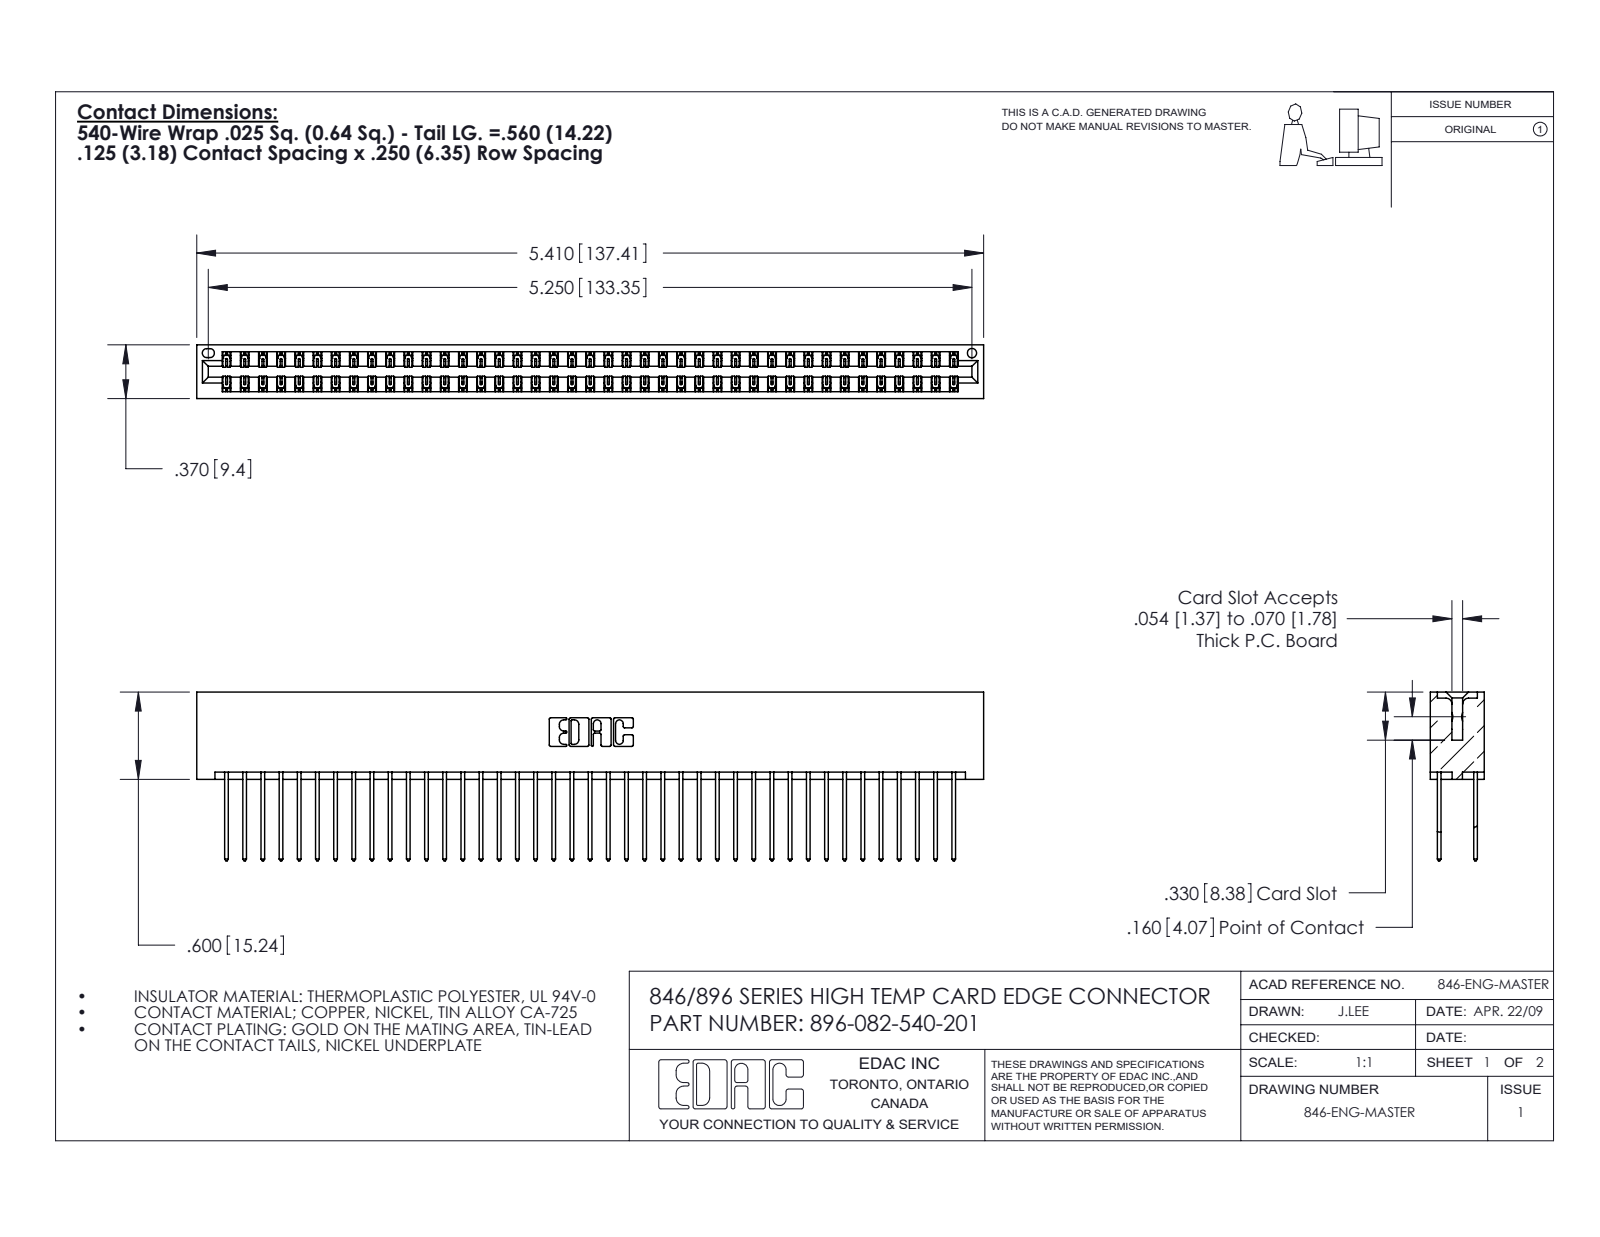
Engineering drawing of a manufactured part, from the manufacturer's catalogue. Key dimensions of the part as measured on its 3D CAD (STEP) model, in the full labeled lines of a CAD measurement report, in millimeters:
Part name (STEP PRODUCT): 396-082-540-201; 346 Part_No Mounting Lugs; 345-292-001_345-293-140
STEP written by: SolidWorks 2016 (CONFIG_CONTROL_DESIGN)
Units: millimetres
Bodies: 83 solids, 4378 faces (2942 planar, 1436 cylindrical, 0 other)
Overall size (bounding box): 137.4 × 29.5 × 9.4
Volume: 14 300 mm³ · Surface area: 21 240 mm²
Round holes (diameter × count): ⌀1.6 ×1
Partial cylindrical surfaces — rounded edges, fillets, slot ends (radius × count): R0.2 ×123, R0.3 ×82, R0.3 ×22, R0.2 ×6, R0.8 ×6, R0.7 ×3, R0.4 ×2, R0.6 ×2
Main face-to-face distances: 1.2, 8.2, 6.4, 1.8, 7.6, 0.6, 9.4, 7, 3.8, 5.6
